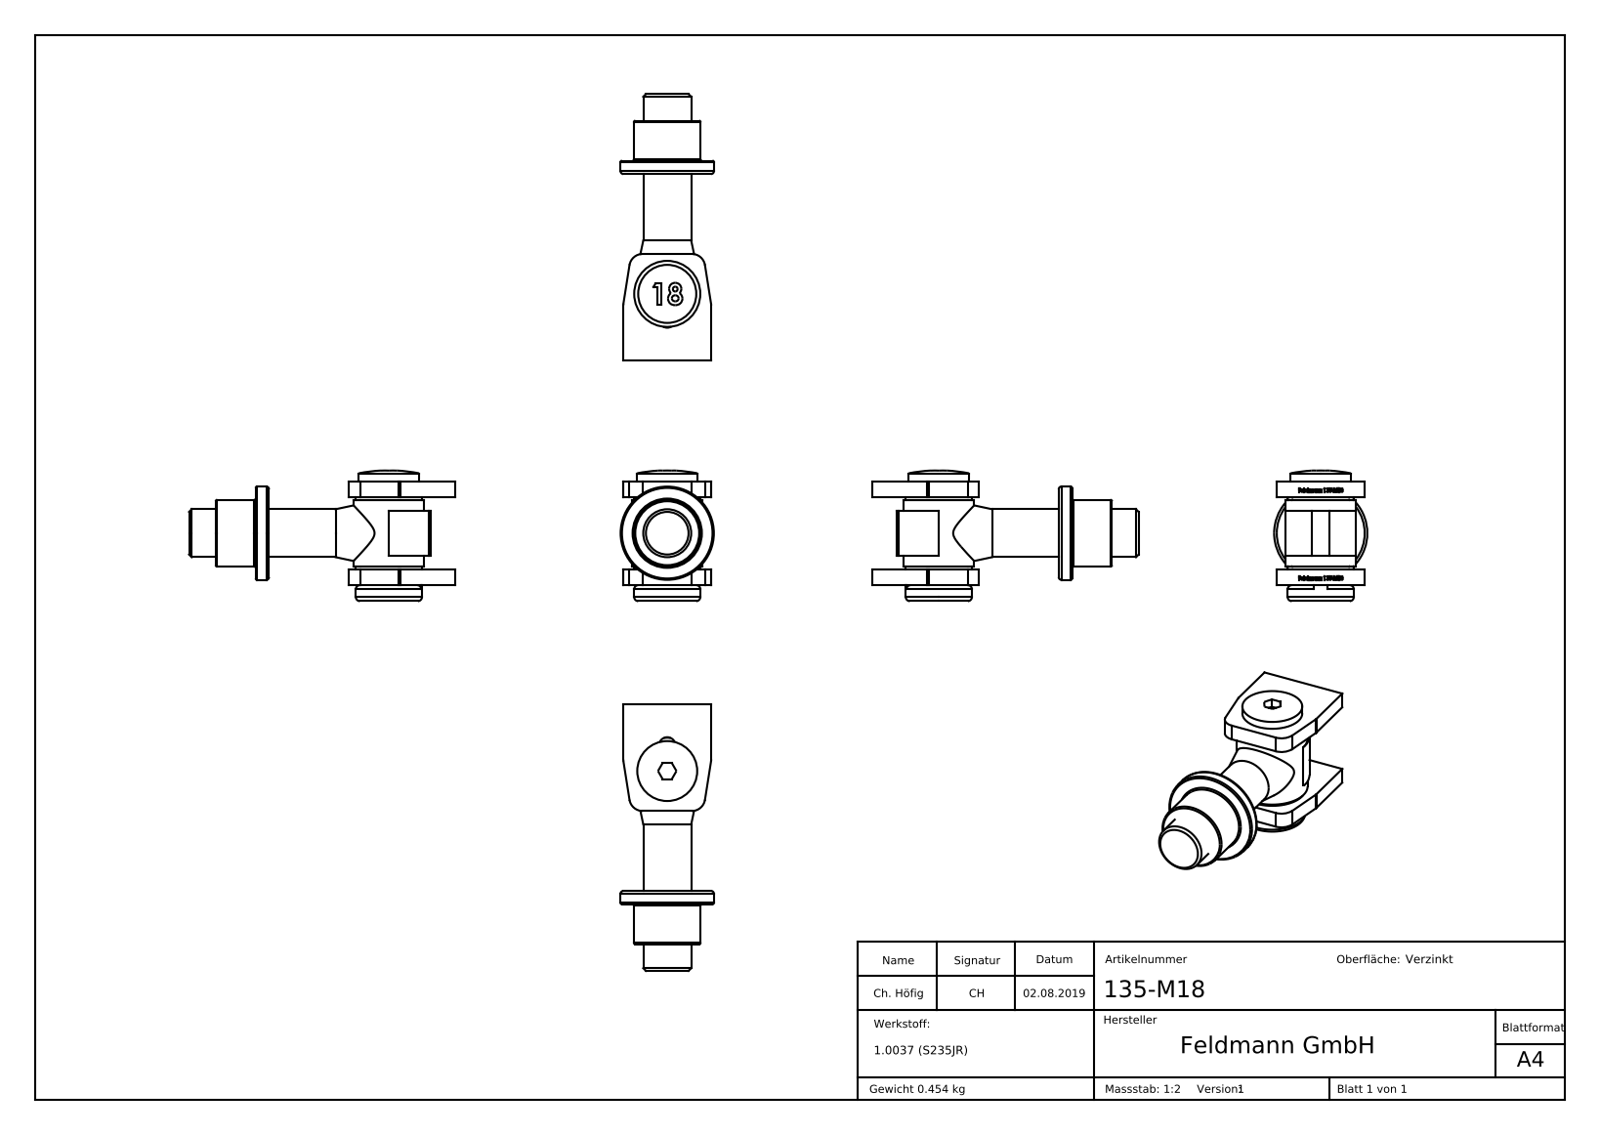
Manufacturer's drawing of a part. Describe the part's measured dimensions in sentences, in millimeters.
The part is named "135-MXX Teil2_135-M18 Teil2; 135-MXX Teil1_135-M18 Teil1; 135-MXX Teil4_135-M18 Teil4; 135-M18 (+3 more)". Its 3-D file was written by "SolidWorks 2015 (CONFIG_CONTROL_DESIGN)". It is 8 solids with 552 faces: 282 planar, 50 cylindrical and 220 other. Overall it measures 100 by 49.02 by 35 millimeters. Its volume is 58 651 cubic millimeters and its surface area 24 741 square millimeters. Round holes: 1 of diameter 6.8, 1 of diameter 9, 1 of diameter 14.9, 1 of diameter 15, 1 of diameter 15.5, 1 of diameter 16. Round bosses or shafts: 2 of diameter 25, 1 of diameter 35, 1 of diameter 26.5, 1 of diameter 24.8, 1 of diameter 22.5, 1 of diameter 18, 1 of diameter 14.5, 1 of diameter 8. Partial cylindrical surfaces (rounded edges, fillets, slot ends): 4 of radius 5, 2 of radius 15, 1 of radius 3.1, 1 of radius 10. The main face-to-face distances are 6, 33, 39, 27, 32, 7, 26, 1, 6.9, 32.1.
